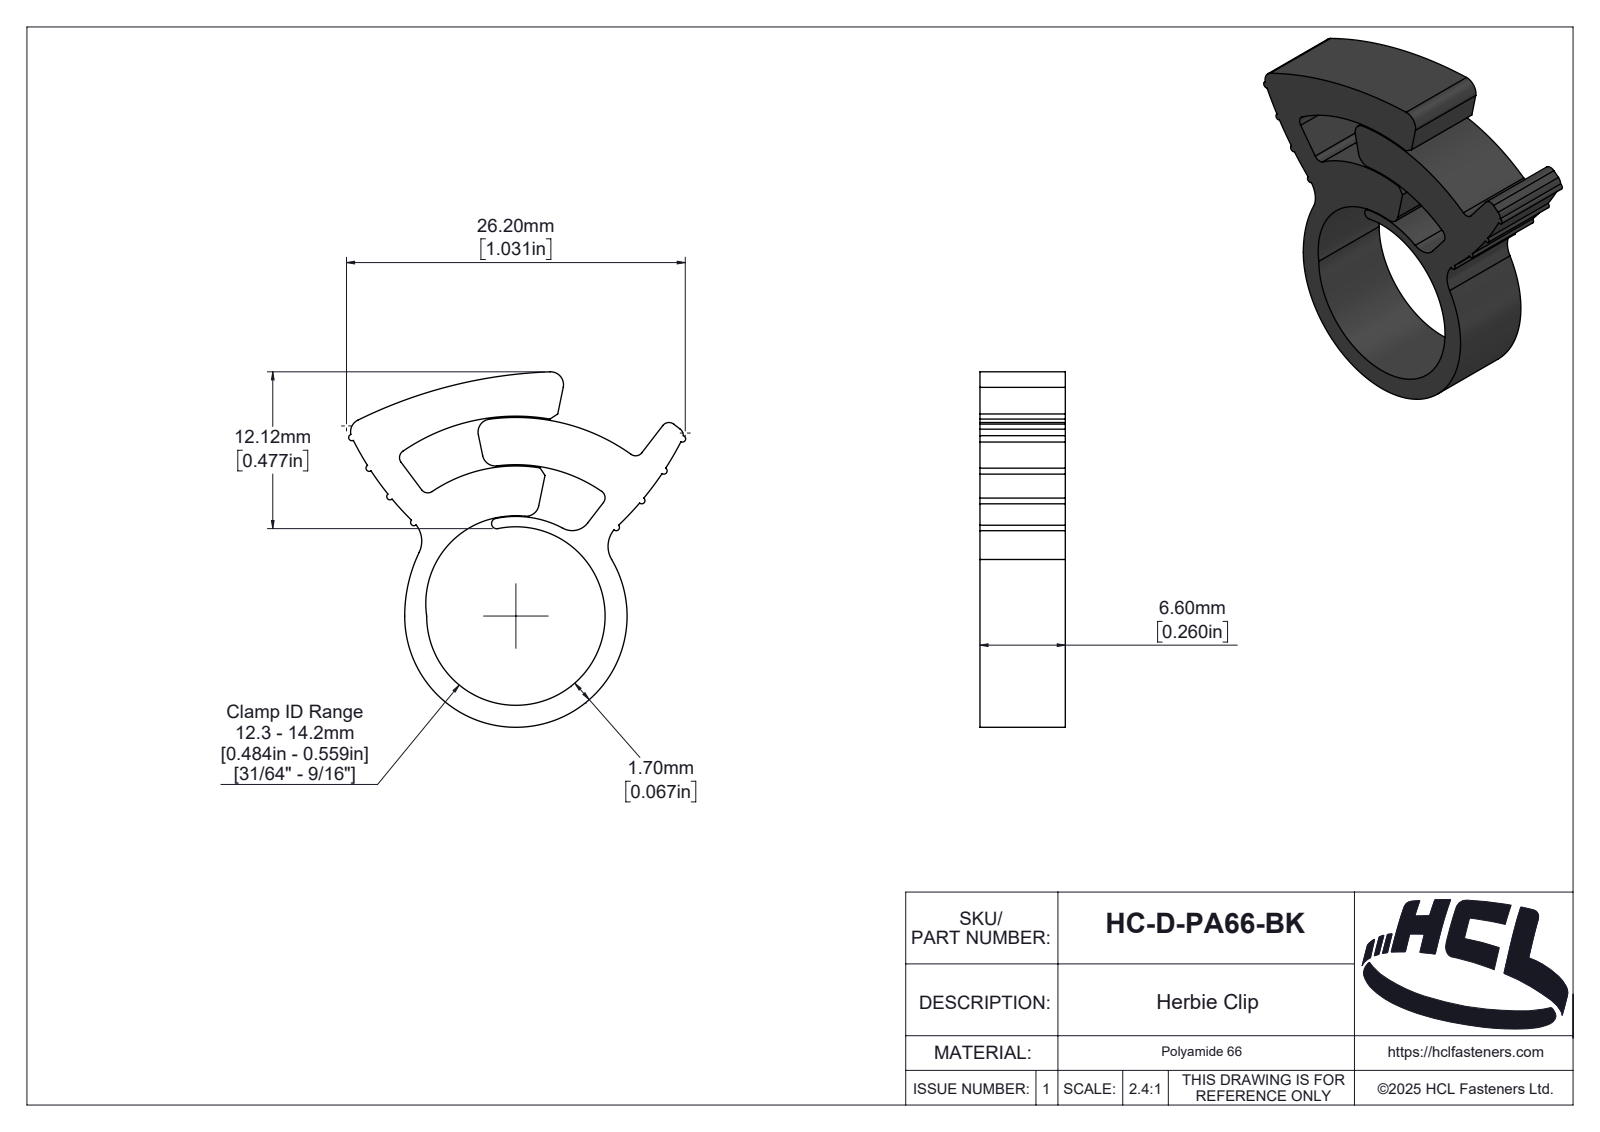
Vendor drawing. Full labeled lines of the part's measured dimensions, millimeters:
Part name (STEP PRODUCT): HC-D-PA66-BK
STEP written by: SolidWorks 2025 (AUTOMOTIVE_DESIGN)
Units: millimetres
Bodies: 1 solid, 162 faces (13 planar, 100 cylindrical, 49 other)
Overall size (bounding box): 27.48 × 26.06 × 6.6
Volume: 1 565 mm³ · Surface area: 1 807 mm²
Partial cylindrical surfaces — rounded edges, fillets, slot ends (radius × count): R0.25 ×8, R0.6 ×6, R1 ×5, R2 ×2, R0.17 ×1, R0.4 ×1, R0.67 ×1, R0.84 ×1
Main face-to-face distances: 6.6
